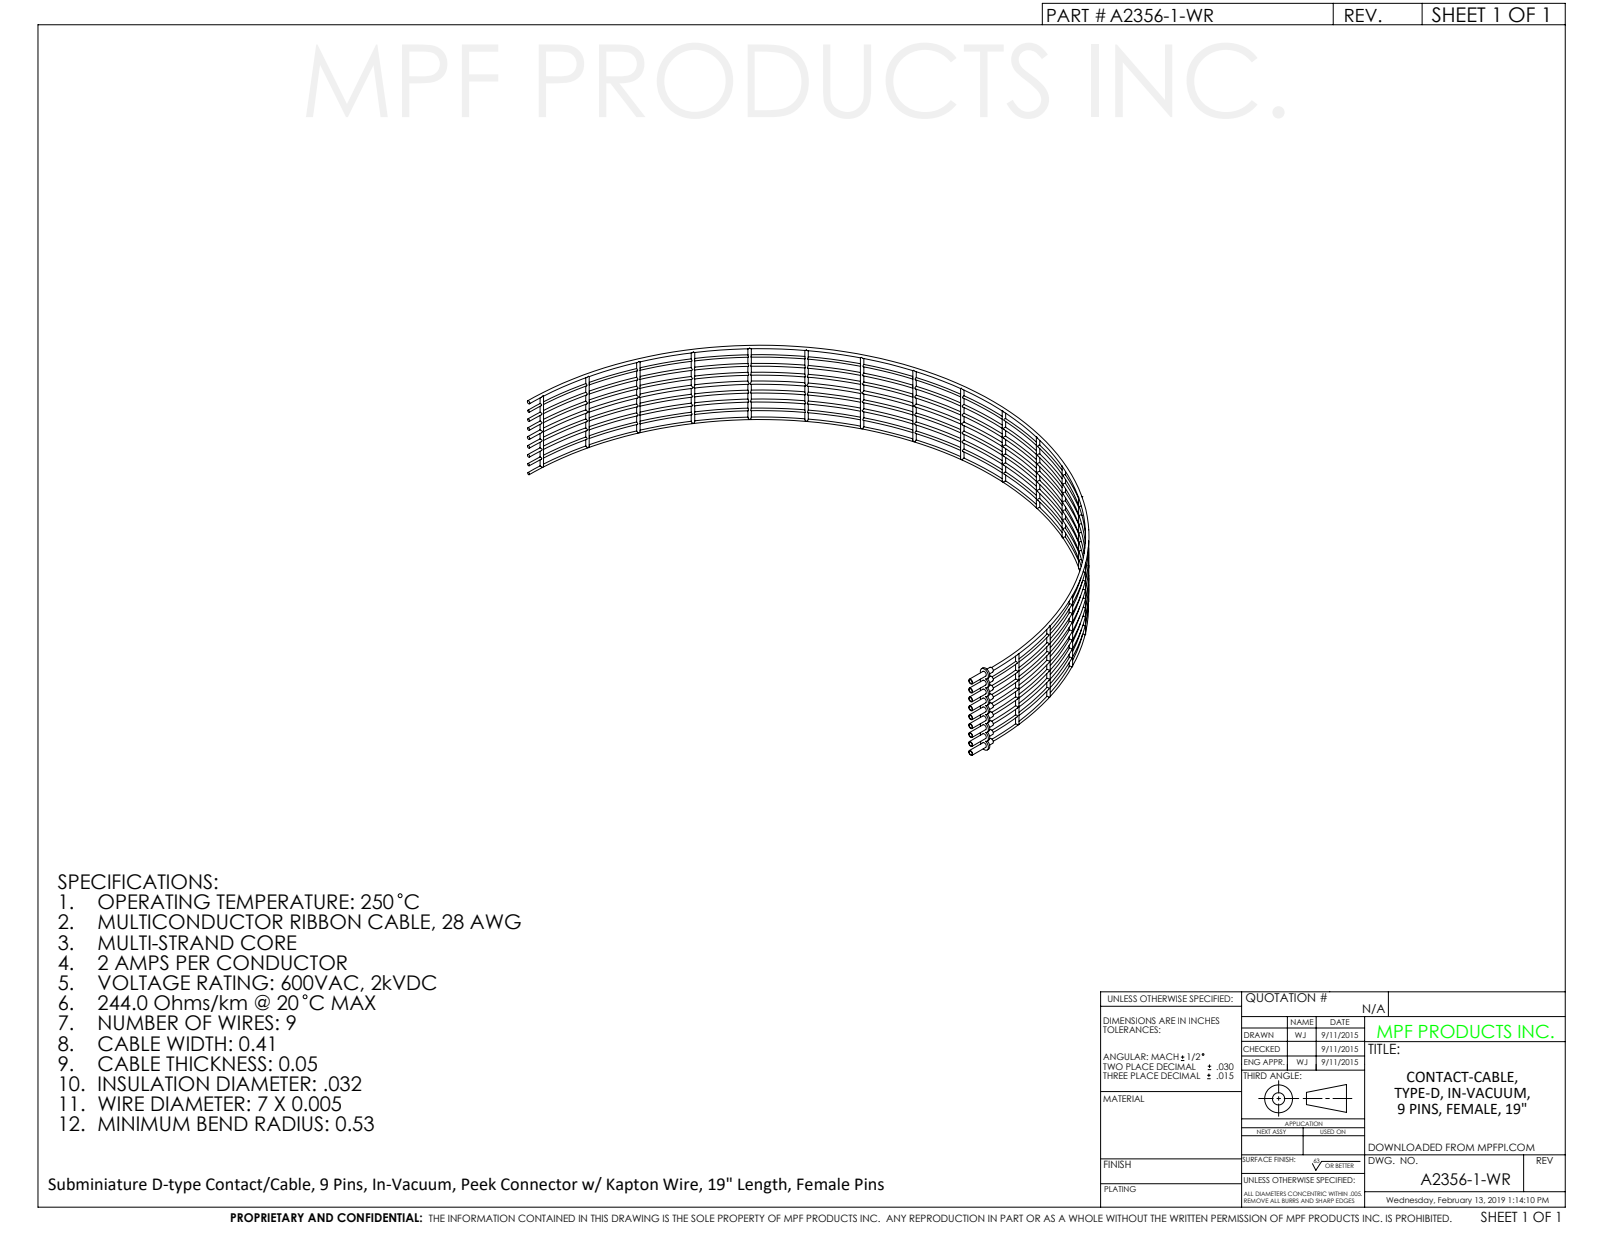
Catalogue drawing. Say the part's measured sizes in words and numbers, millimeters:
The part is named "A2356-1-WR". Its 3-D file was written by "SolidWorks 2012 (CONFIG_CONTROL_DESIGN)". It is 1 solid with 515 faces: 75 planar, 116 cylindrical and 324 other. Overall it measures 154.1 by 83.4 by 23 millimeters. Its volume is 1 000 cubic millimeters and its surface area 5 619 square millimeters. Round holes: 9 of diameter 1. Round bosses or shafts: 18 of diameter 0.8, 9 of diameter 1.3, 8 of diameter 2.7. Partial cylindrical surfaces (rounded edges, fillets, slot ends): 1 of radius 1.3. The main face-to-face distances are 0.5, 1.9, 2.3, 4, 2.2, 1.7, 6.8, 5, 4.5, 2.8. The hole center spacings are 2.5, 5.1, 7.6, 10.2, 12.7, 15.2, 17.8, 20.3.
